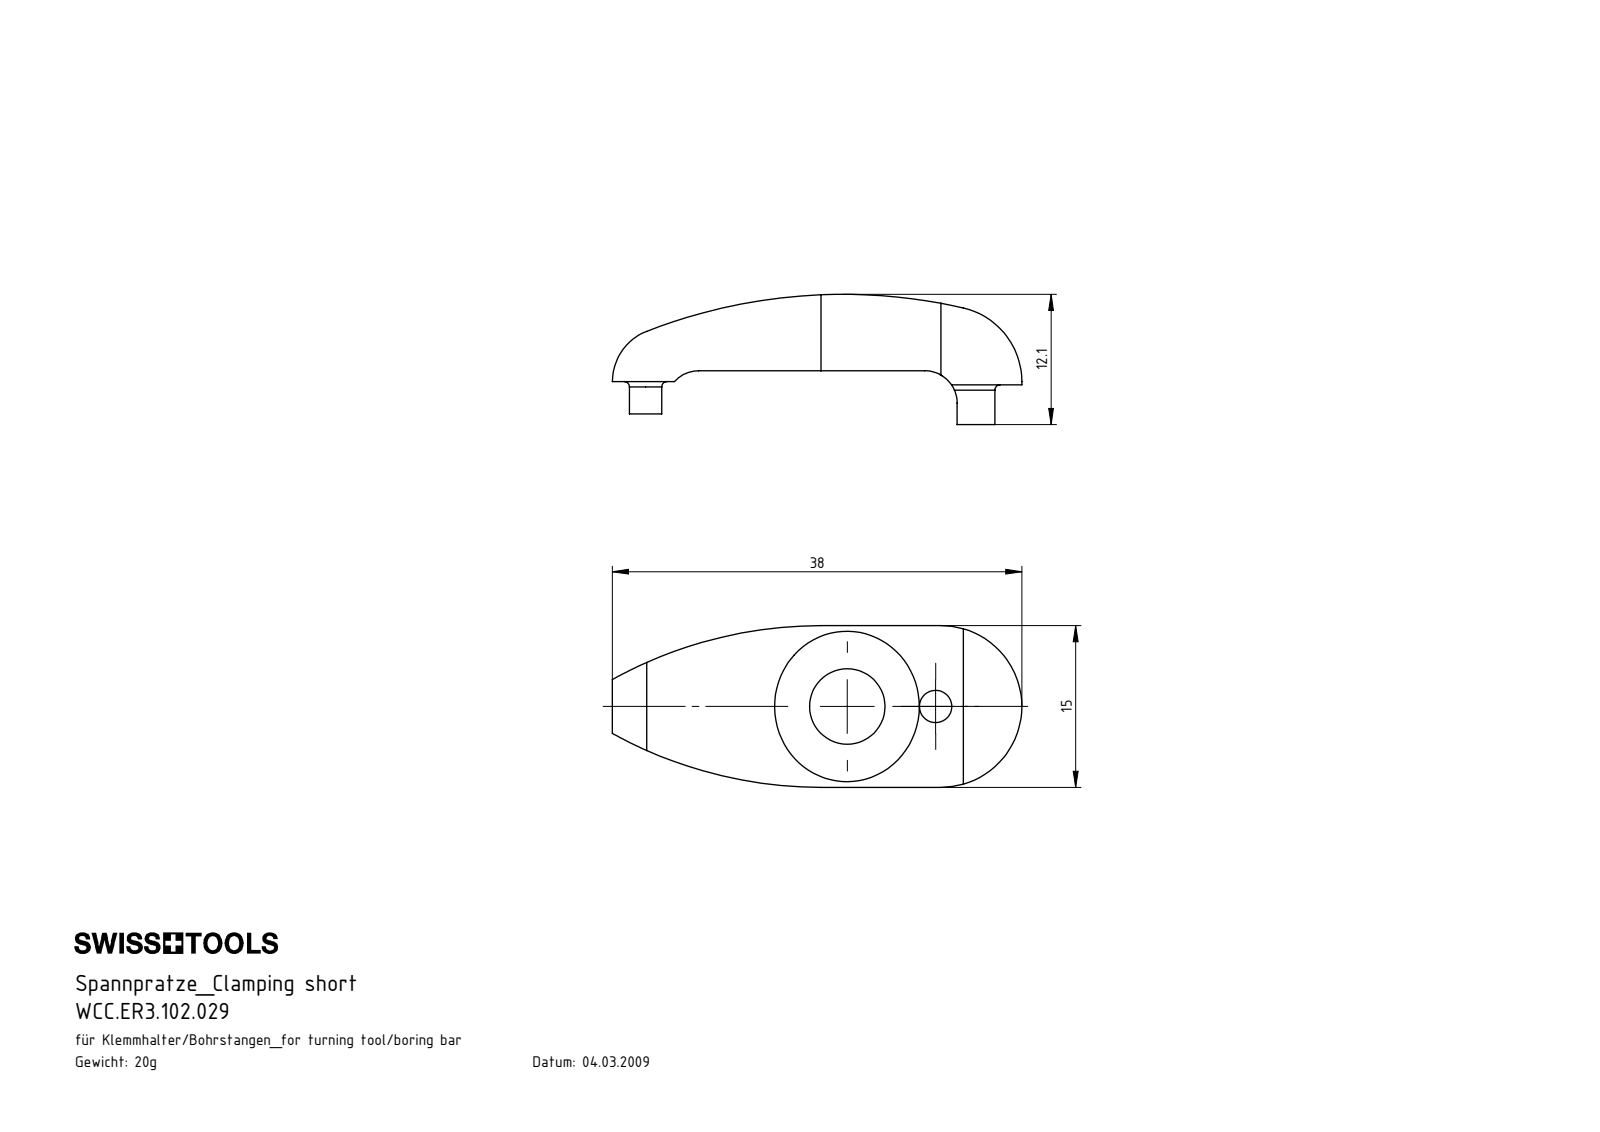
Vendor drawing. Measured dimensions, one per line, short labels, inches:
name: WCC.ER3.102.029
written by: SolidWorks 2017 (AUTOMOTIVE_DESIGN)
unit: in
bodies: 1 solid, 23 faces (8 planar, 12 cylindrical, 3 other)
size: 1.496 × 0.591 × 0.476
volume: 0.153 in³; area: 2.607 in²
holes: 1× ⌀0.118, 1× ⌀0.276
bosses: 1× ⌀0.157, 1× ⌀0.118
rounds: 2× R0.118, 2× R1.575, 1× R0.197, 1× R0.276, 1× R0.295, 1× R1.969
face distances: 0.591, 0.051, 0.039, 0.157, 0.146, 0.197, 0.106, 0.118
hole spacings: 0.323
